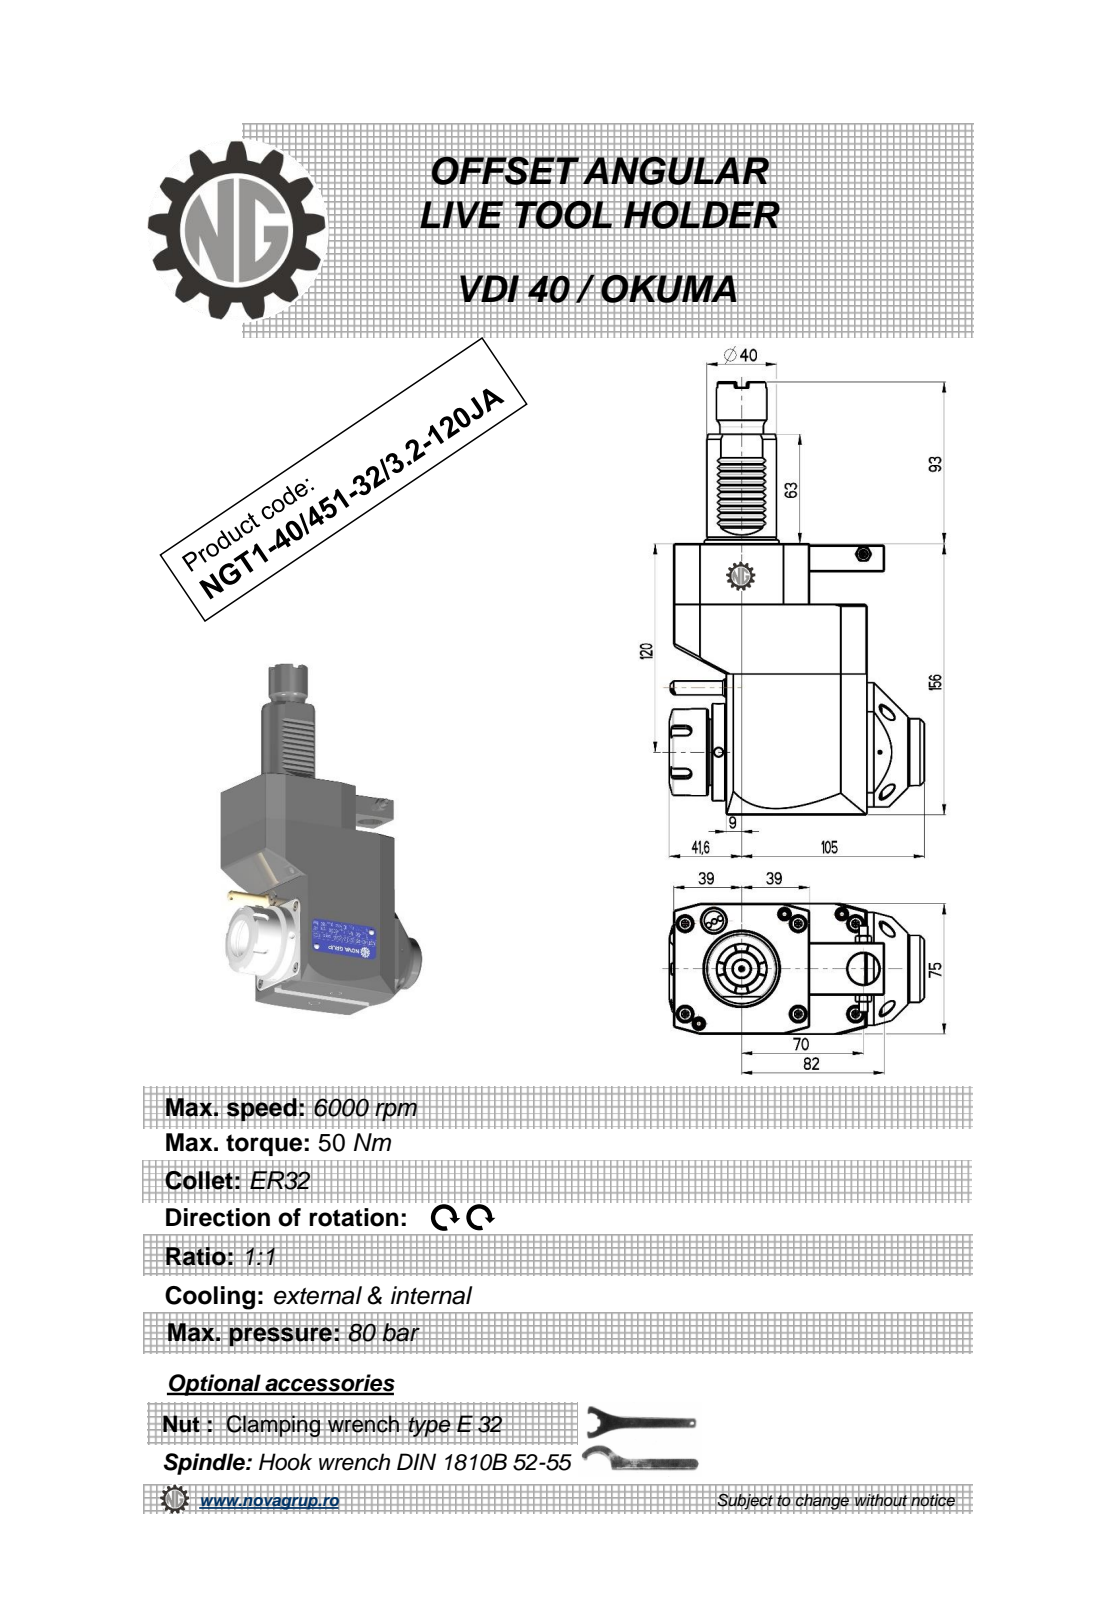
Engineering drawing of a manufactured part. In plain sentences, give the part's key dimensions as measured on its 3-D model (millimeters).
The part is named "NGT1_40_451_32_3_2_120JA". Its 3-D file was written by "PRO/ENGINEER BY PARAMETRIC TECHNOLOGY CORPORATION, 2010280 (CONFIG_CONTROL_DESIGN)". It is 1 solid with 482 faces: 217 planar, 91 cylindrical and 174 other. Overall it measures 249 by 146.6 by 75 millimeters. Its volume is 1 244 000 cubic millimeters and its surface area 94 450 square millimeters. Round holes: 3 of diameter 5, 1 of diameter 3, 1 of diameter 4.2, 1 of diameter 9.5, 1 of diameter 18, 1 of diameter 27. Round bosses or shafts: 1 of diameter 56, 1 of diameter 50, 1 of diameter 43, 1 of diameter 40, 1 of diameter 38.5, 1 of diameter 29, 1 of diameter 25, 1 of diameter 10. Partial cylindrical surfaces (rounded edges, fillets, slot ends): 12 of radius 0.26, 10 of radius 0.3, 6 of radius 0.2, 5 of radius 3, 1 of radius 0.5, 1 of radius 10, 1 of radius 40. The main face-to-face distances are 75, 156, 111, 33, 121, 30, 35, 81, 93.43, 78. The hole center spacings are 40.93, 77.5, 83.25, 112.5, 141.16.
